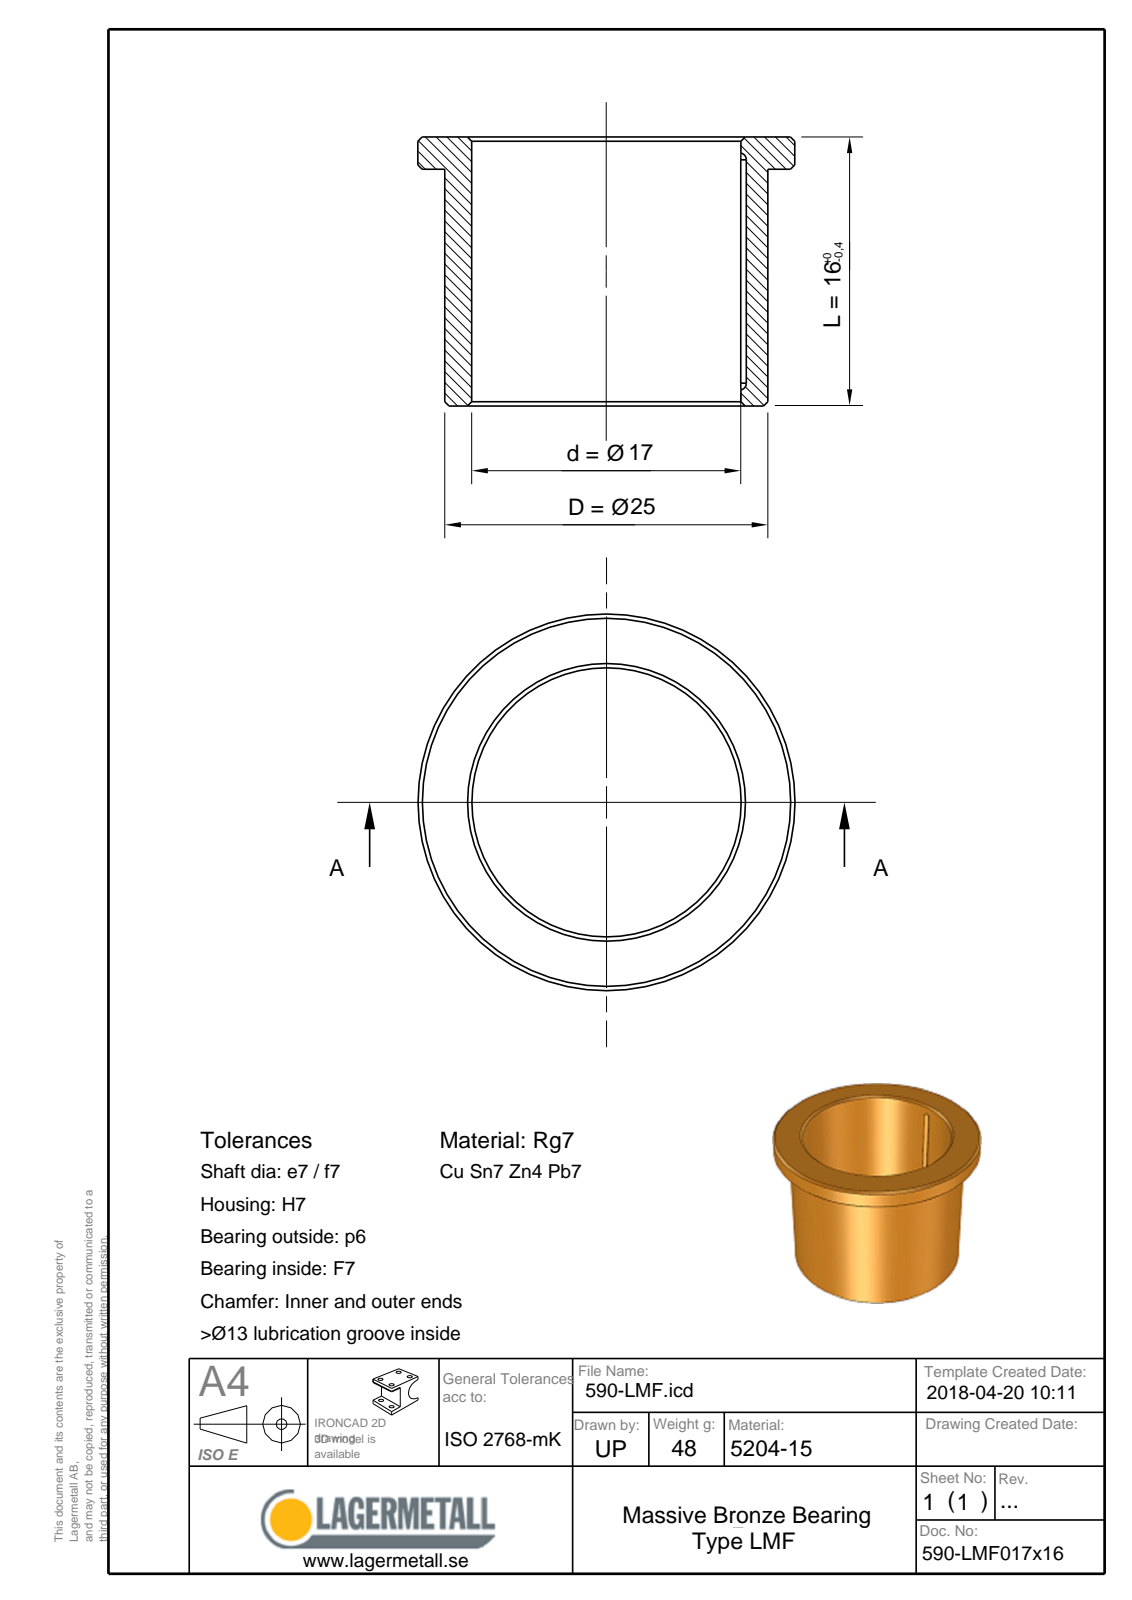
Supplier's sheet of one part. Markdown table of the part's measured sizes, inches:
| quantity | value |
| --- | --- |
| part name | 590-LMF017x16 |
| STEP written by | Spatial InterOp 3D (CONFIG_CONTROL_DESIGN) |
| units | inches |
| bodies | 1 solid, 18 faces (5 planar, 6 cylindrical, 7 other) |
| overall size | 1.26 × 1.26 × 0.63 |
| volume | 0.33 in³ |
| surface area | 5.045 in² |
| round holes (diameter × count) | 0.669 × 1 |
| round bosses / shafts (diameter × count) | 1.26 × 1, 0.984 × 1 |
| partial cylindrical surfaces (radius × count) | 0.03 × 3 |
| main face-to-face distances | 0.157, 0.472, 0.63, 0.059 |
